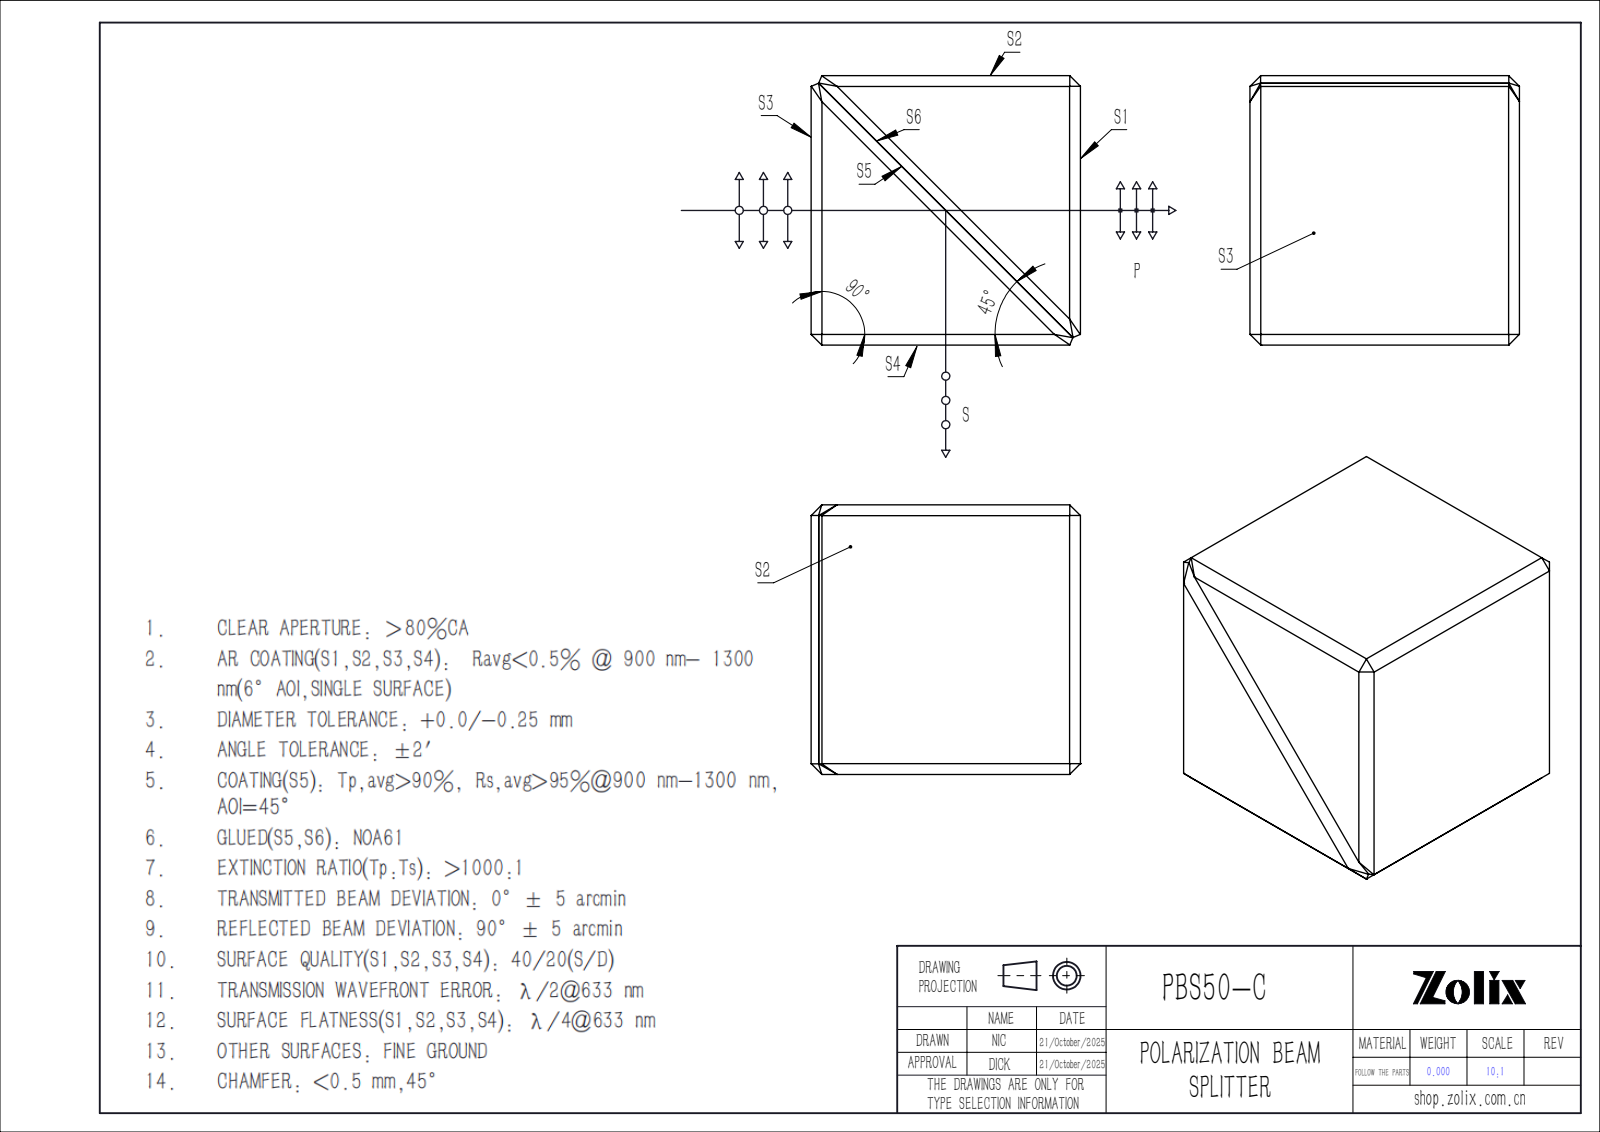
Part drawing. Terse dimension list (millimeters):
name: 50.8 mm
written by: SolidWorks 2021 (CONFIG_CONTROL_DESIGN)
unit: mm
bodies: 2 solids, 43 faces (41 planar, 2 cylindrical, 0 other)
size: 50.8 × 50.8 × 50.8
volume: 131 073 mm³; area: 22 668 mm²
holes: 1× ⌀1.2
face distances: 50.8, 71.55, 35.64, 35.77, 71.54, 50.65, 50.66, 50.51, 45.8, 5
